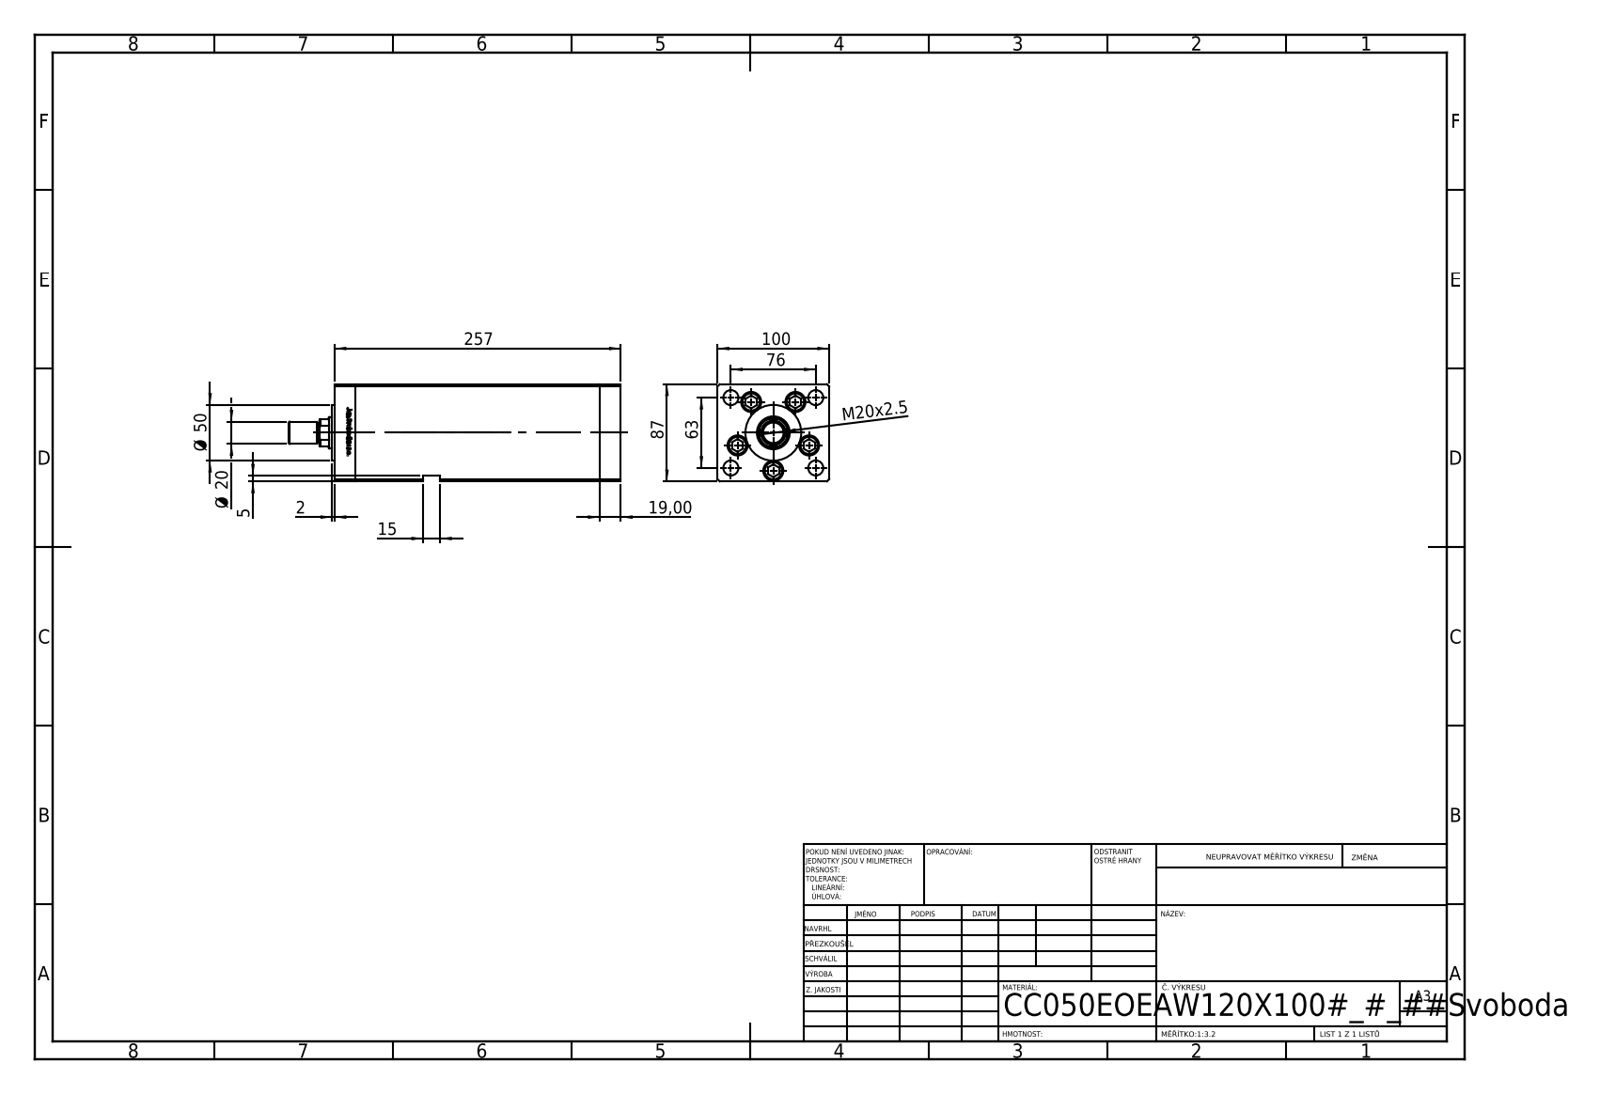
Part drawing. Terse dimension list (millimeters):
name: V220C_FRONT_E; ALLEN BOLT; V220C BACK_E; V220C_E MIDDLE (+2 more)
written by: SolidWorks 2019 (CONFIG_CONTROL_DESIGN)
unit: mm
bodies: 15 solids, 1228 faces (479 planar, 169 cylindrical, 580 other)
size: 297.5 × 100 × 87
volume: 1 874 000 mm³; area: 268 344 mm²
holes: 11× ⌀13.5, 5× ⌀18, 5× ⌀18.5, 4× ⌀12.5, 2× ⌀2, 2× ⌀13.16, 1× ⌀28, 1× ⌀29.5
bosses: 5× ⌀17, 5× ⌀8, 1× ⌀50, 1× ⌀20, 1× ⌀18
rounds: 2× R0.93, 1× R13.5
face distances: 100, 87, 19, 218.5, 237.5, 256.5, 34.25, 15.25, 203.25, 222.25
hole spacings: 34, 18.59, 39.64, 49.36, 57.95, 21.03, 38.08, 39.27
